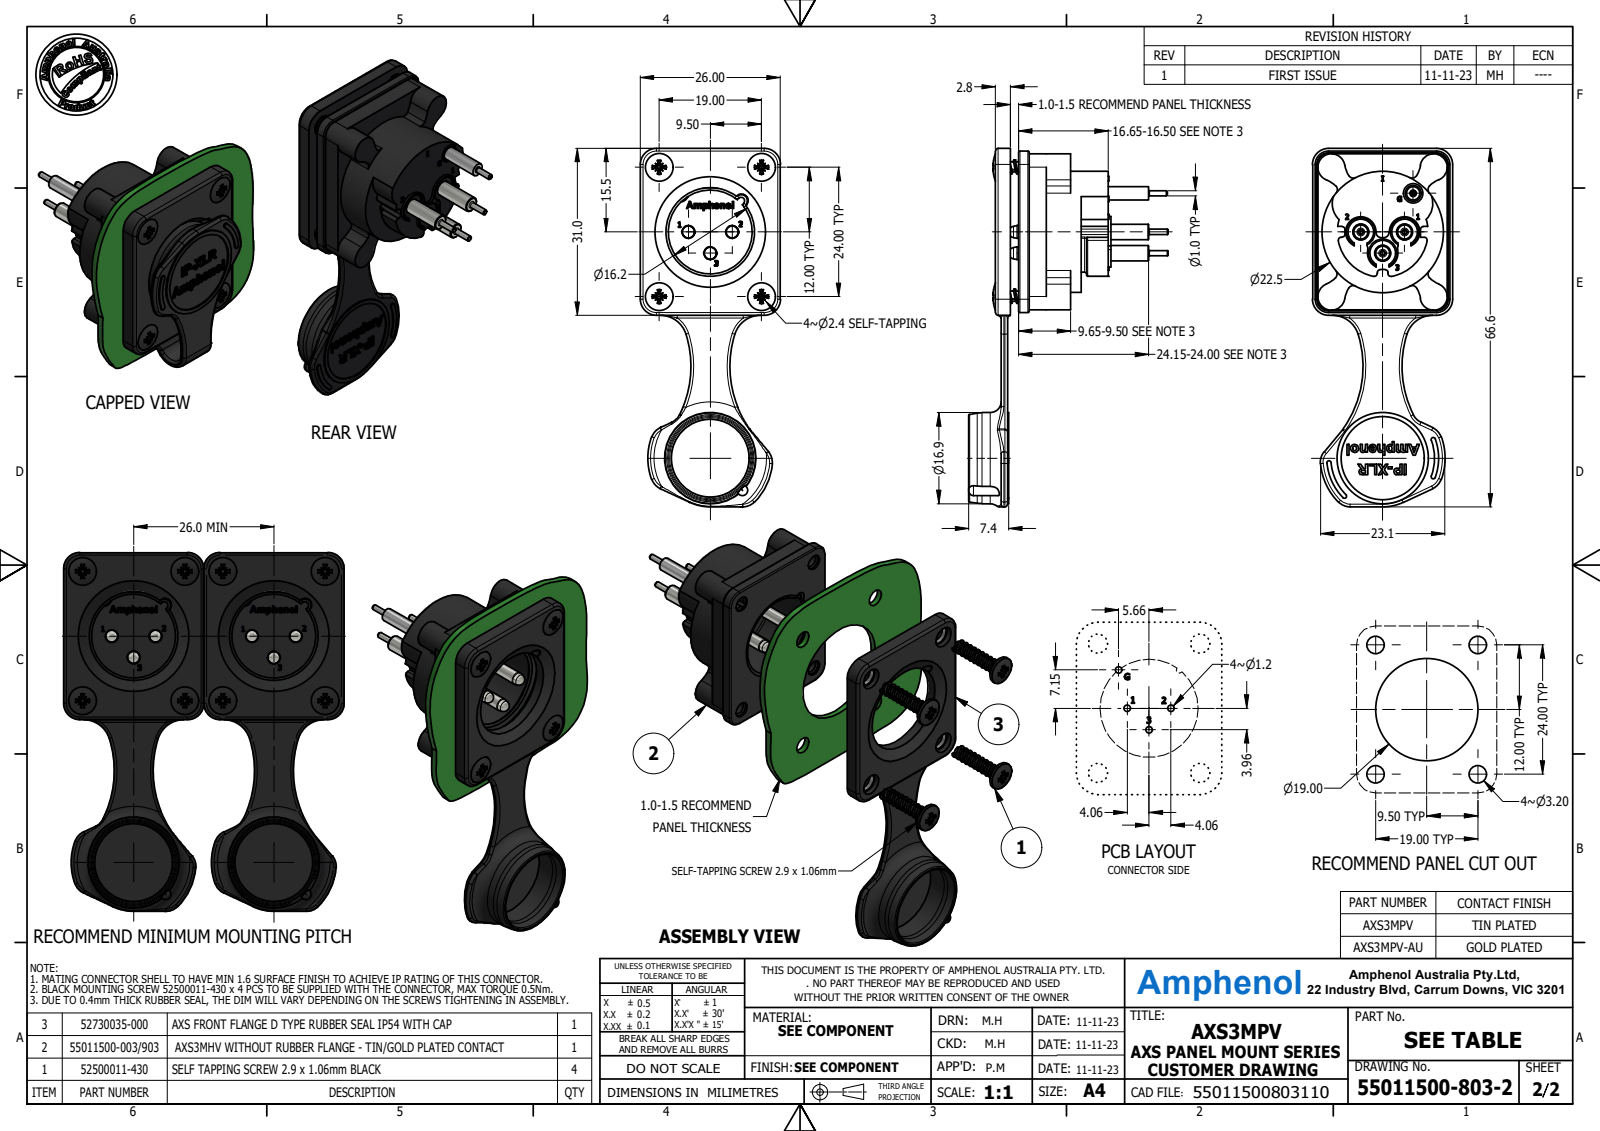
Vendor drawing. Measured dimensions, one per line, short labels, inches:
name: AXS3MPV
written by: Autodesk Inventor 2022 (AUTOMOTIVE_DESIGN)
unit: in
bodies: 1 solid, 2052 faces (481 planar, 430 cylindrical, 1141 other)
size: 2.62 × 1.445 × 1.024
volume: 0.536 in³; area: 13.53 in²
holes: 7× ⌀0.094, 4× ⌀0.116, 4× ⌀0.134, 4× ⌀0.157, 3× ⌀0.115, 3× ⌀0.187, 1× ⌀0.087, 1× ⌀0.102, 1× ⌀0.142, 1× ⌀0.567, 1× ⌀0.606, 1× ⌀0.638
bosses: 4× ⌀0.205, 4× ⌀0.039, 3× ⌀0.112, 3× ⌀0.093, 1× ⌀0.886, 1× ⌀0.669, 1× ⌀0.665, 1× ⌀0.118
rounds: 23× R0.02, 14× R0.039, 12× R0.016, 12× R0.045, 10× R0.118, 10× R0.197, 8× R0.01, 8× R0.098
face distances: 0.047, 0.069, 0.022, 0.157, 0.089, 0.11, 0.041, 0.116, 0.449, 0.02
hole spacings: 0.519, 0.603, 0.713, 0.16, 0.223, 0.49, 0.731, 0.748
